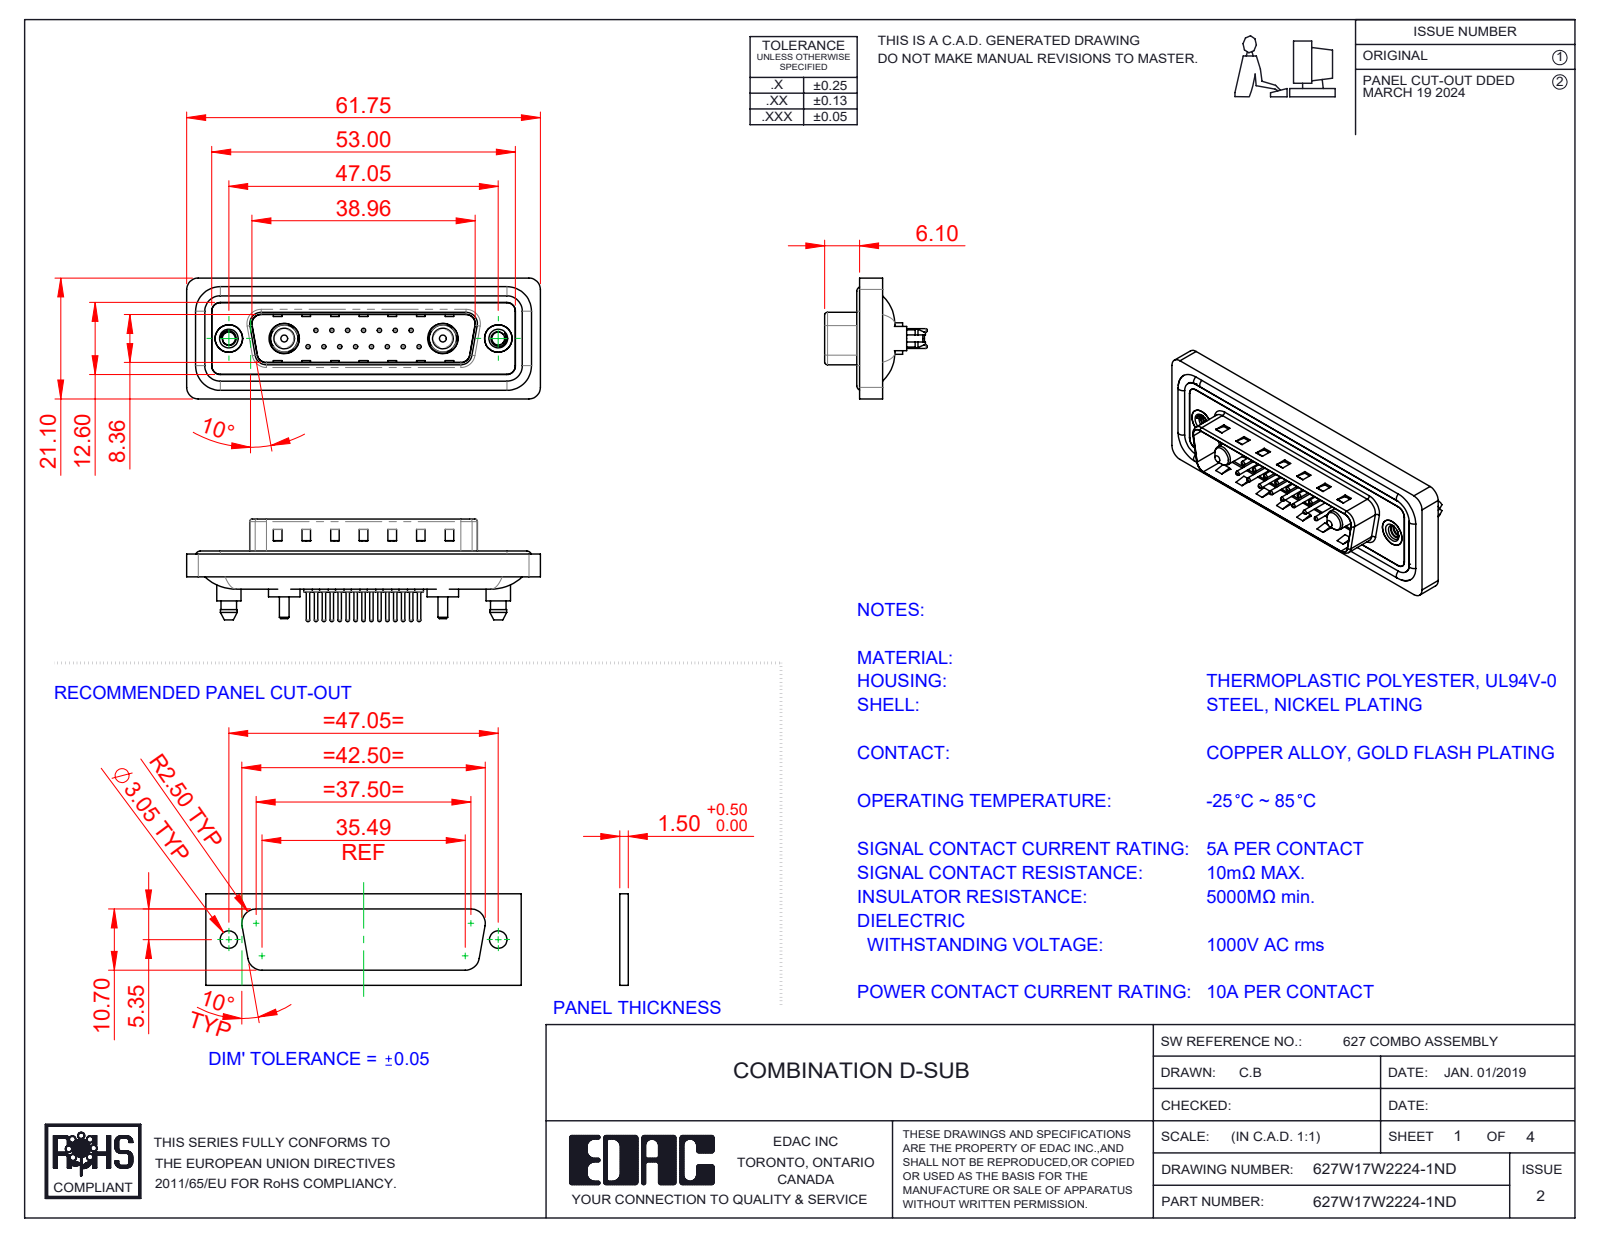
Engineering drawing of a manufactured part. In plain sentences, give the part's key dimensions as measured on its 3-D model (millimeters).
The part is named "627Combo Contact Row 1_24; 627Combo Threaded Boardlock_D; Power Pin_10A S; 627Combo Shell Front_25 Contacts (+6 more)". Its 3-D file was written by "SolidWorks 2023 (CONFIG_CONTROL_DESIGN)". It is 26 solids with 1174 faces: 350 planar, 476 cylindrical and 348 other. Overall it measures 61.75 by 21.1 by 17.9 millimeters. Its volume is 7 372 cubic millimeters and its surface area 12 225 square millimeters. Round holes: 15 of diameter 0.75, 15 of diameter 1.6, 15 of diameter 2, 2 of diameter 2.26, 2 of diameter 4, 2 of diameter 4.8, 2 of diameter 4.85, 2 of diameter 5, 2 of diameter 5.3. Round bosses or shafts: 15 of diameter 1.5, 15 of diameter 0.6, 4 of diameter 1.6, 2 of diameter 5.5, 2 of diameter 5.4, 2 of diameter 5.2, 2 of diameter 4.9, 2 of diameter 4.75. Partial cylindrical surfaces (rounded edges, fillets, slot ends): 24 of radius 1.5, 18 of radius 2, 10 of radius 1.6, 8 of radius 0.5, 4 of radius 0.25, 4 of radius 0.6, 4 of radius 0.65, 4 of radius 0.9. The main face-to-face distances are 0.4, 1.5, 1.1, 1.6, 0.5, 3.1, 2.9, 0.82, 9.58, 4.1. The hole center spacings are 3.16, 2.77, 5.54, 8.31, 5.04, 7.49, 11.08, 5.03.
